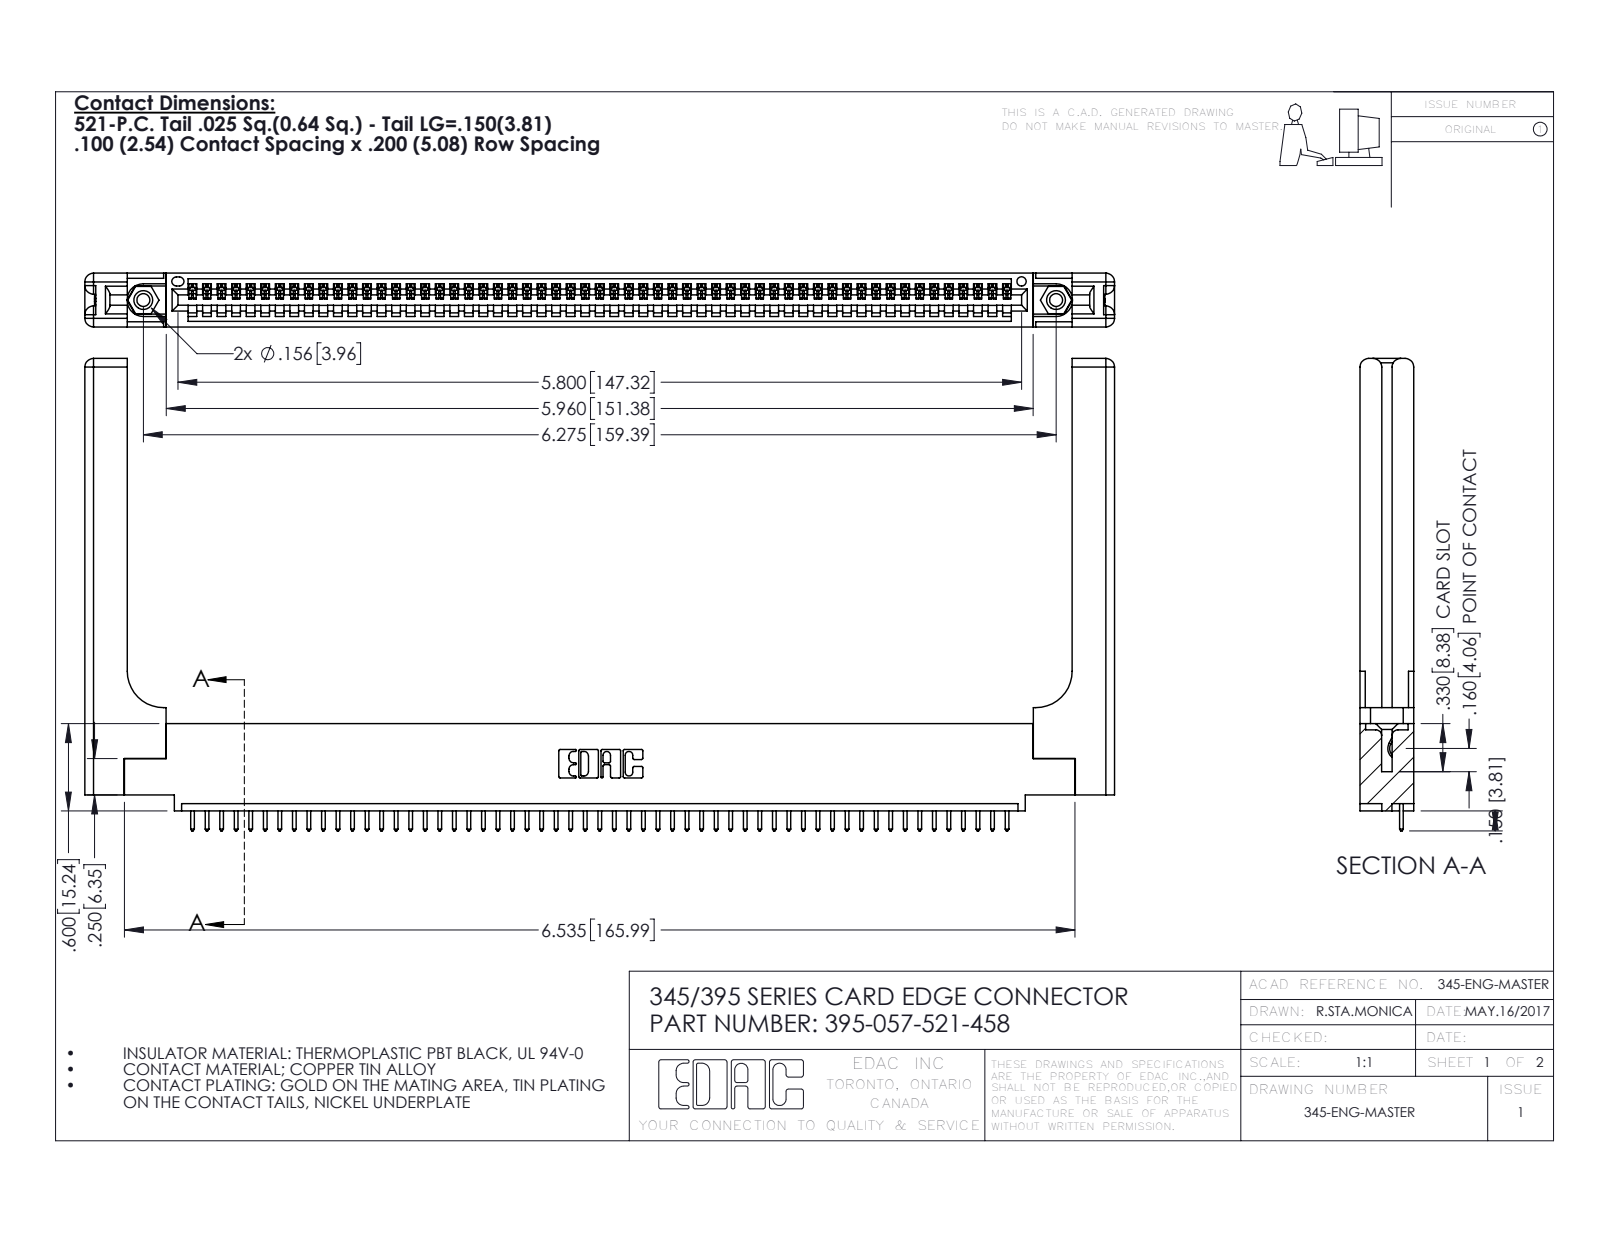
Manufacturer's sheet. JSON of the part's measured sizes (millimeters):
{"part_name": "395-057-521-458; 345-250-001_345-250-001-102; 345-292-001_345-293-121; 345-220-058_345-220-058 (+1 more)", "step_written_by": "SolidWorks 2016 (CONFIG_CONTROL_DESIGN)", "units": "millimeters", "bodies": {"solids": 62, "faces": 3692, "planar": 2512, "cylindrical": 1120, "other": 60}, "overall_size": [179.8, 82.5, 9.4], "volume_mm3": 25470, "surface_area_mm2": 27500, "round_holes": [[2.3, 2], [3.2, 2], [4, 2], [1.6, 1]], "round_bosses_or_shafts": [[3.9, 2]], "partial_cylinders_radius": [[0.2, 114], [0.3, 114], [0.3, 22], [1.5, 16], [0.2, 6], [0.8, 6], [0.7, 3], [0.8, 2]], "face_to_face_distances": [1.8, 9.4, 7.6, 2.5, 6.9, 0.6, 5.1, 5.7, 3.8, 3.8], "hole_center_spacings": [6.9, 153.4, 159.4]}
